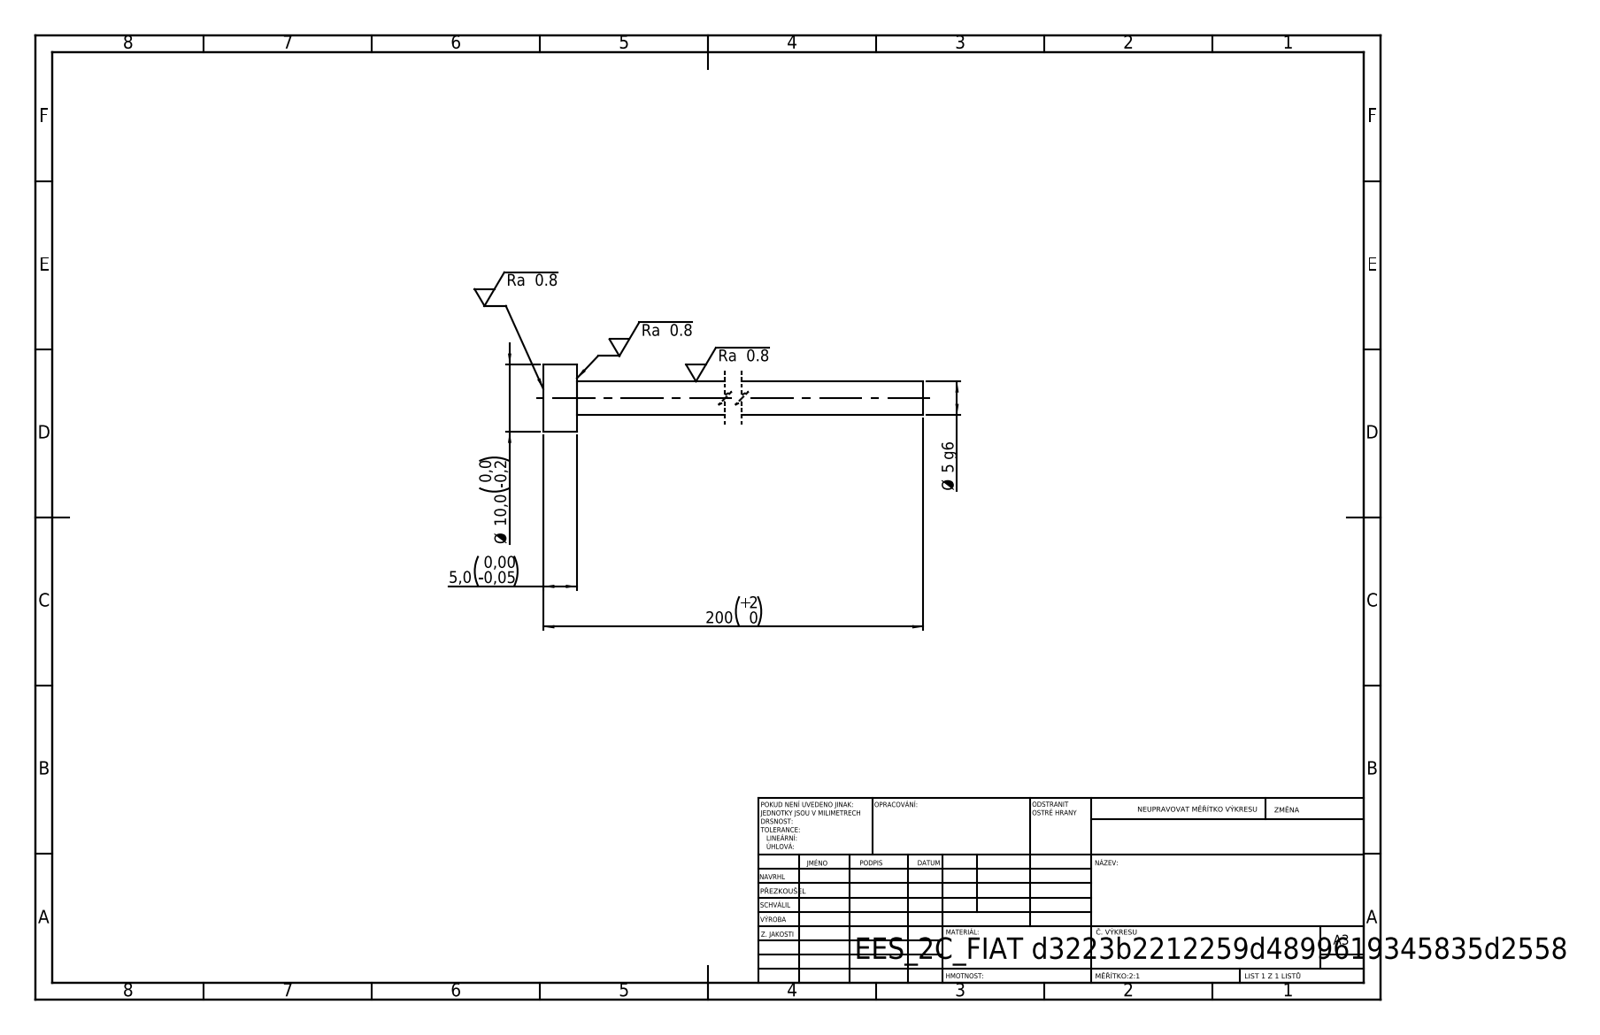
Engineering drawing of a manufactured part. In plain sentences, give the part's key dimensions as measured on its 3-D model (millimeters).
Its 3-D file was written by "SolidWorks 2019 (CONFIG_CONTROL_DESIGN)". It is 1 solid with 7 faces: 3 planar, 4 cylindrical and 0 other. Overall it measures 200 by 10 by 10 millimeters. Its volume is 4 222 cubic millimeters and its surface area 3 377 square millimeters. Round bosses or shafts: 1 of diameter 10, 1 of diameter 5. The main face-to-face distances are 5, 200, 195.
